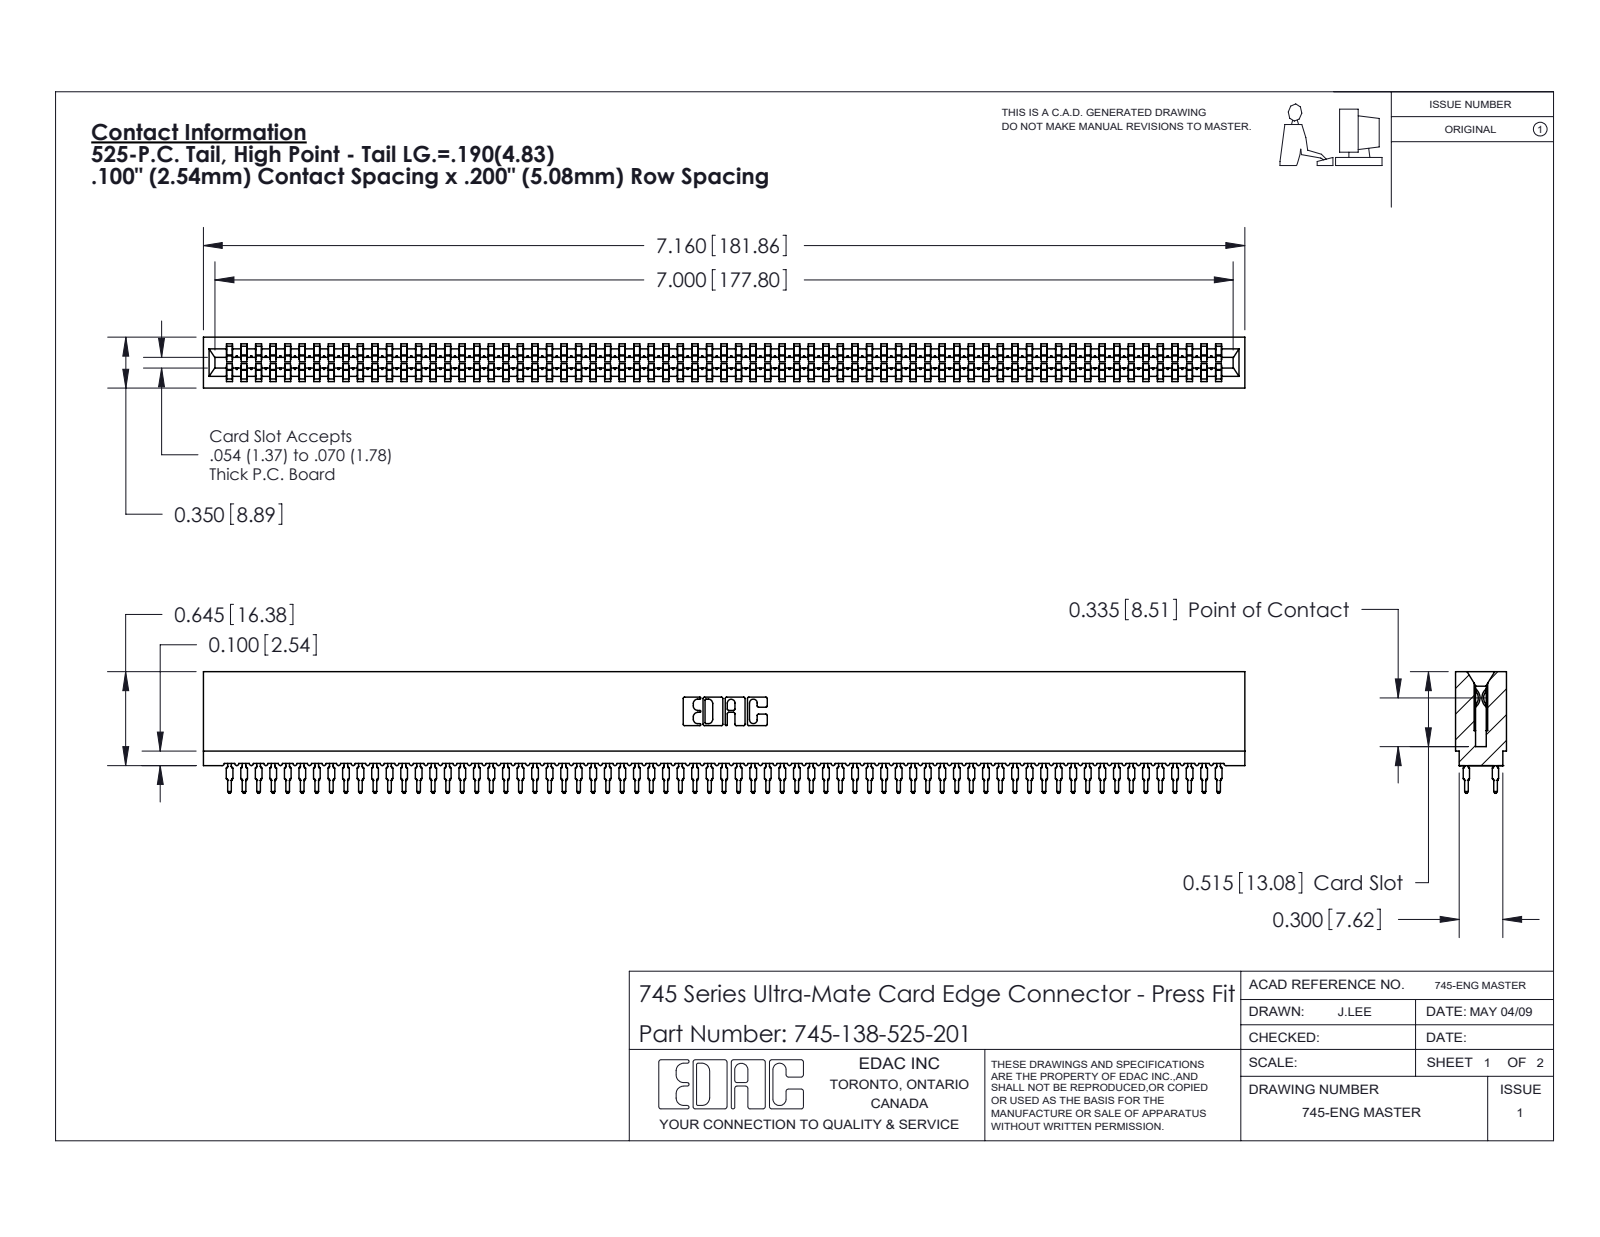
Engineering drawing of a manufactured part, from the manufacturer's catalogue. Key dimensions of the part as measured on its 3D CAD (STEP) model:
Part name (STEP PRODUCT): 745 Part_Insulator Option - 01; 745-138-525-201; 745-292-001_525
STEP written by: SolidWorks 2020 (CONFIG_CONTROL_DESIGN)
Units: inches
Bodies: 139 solids, 12446 faces (6403 planar, 2455 cylindrical, 3588 other)
Overall size (bounding box): 7.16 × 0.836 × 0.35
Volume: 0.987 in³ · Surface area: 51.75 in²
Partial cylindrical surfaces — rounded edges, fillets, slot ends (radius × count): R0.021 ×276, R0.015 ×138, R0.01 ×22, R0.005 ×8, R0.011 ×8, R0.007 ×6, R0.031 ×6, R0.026 ×3
Main face-to-face distances: 0.35, 0.063, 0.287, 0.045, 0.305, 0.018, 0.243, 0.138, 0.212, 0.093
